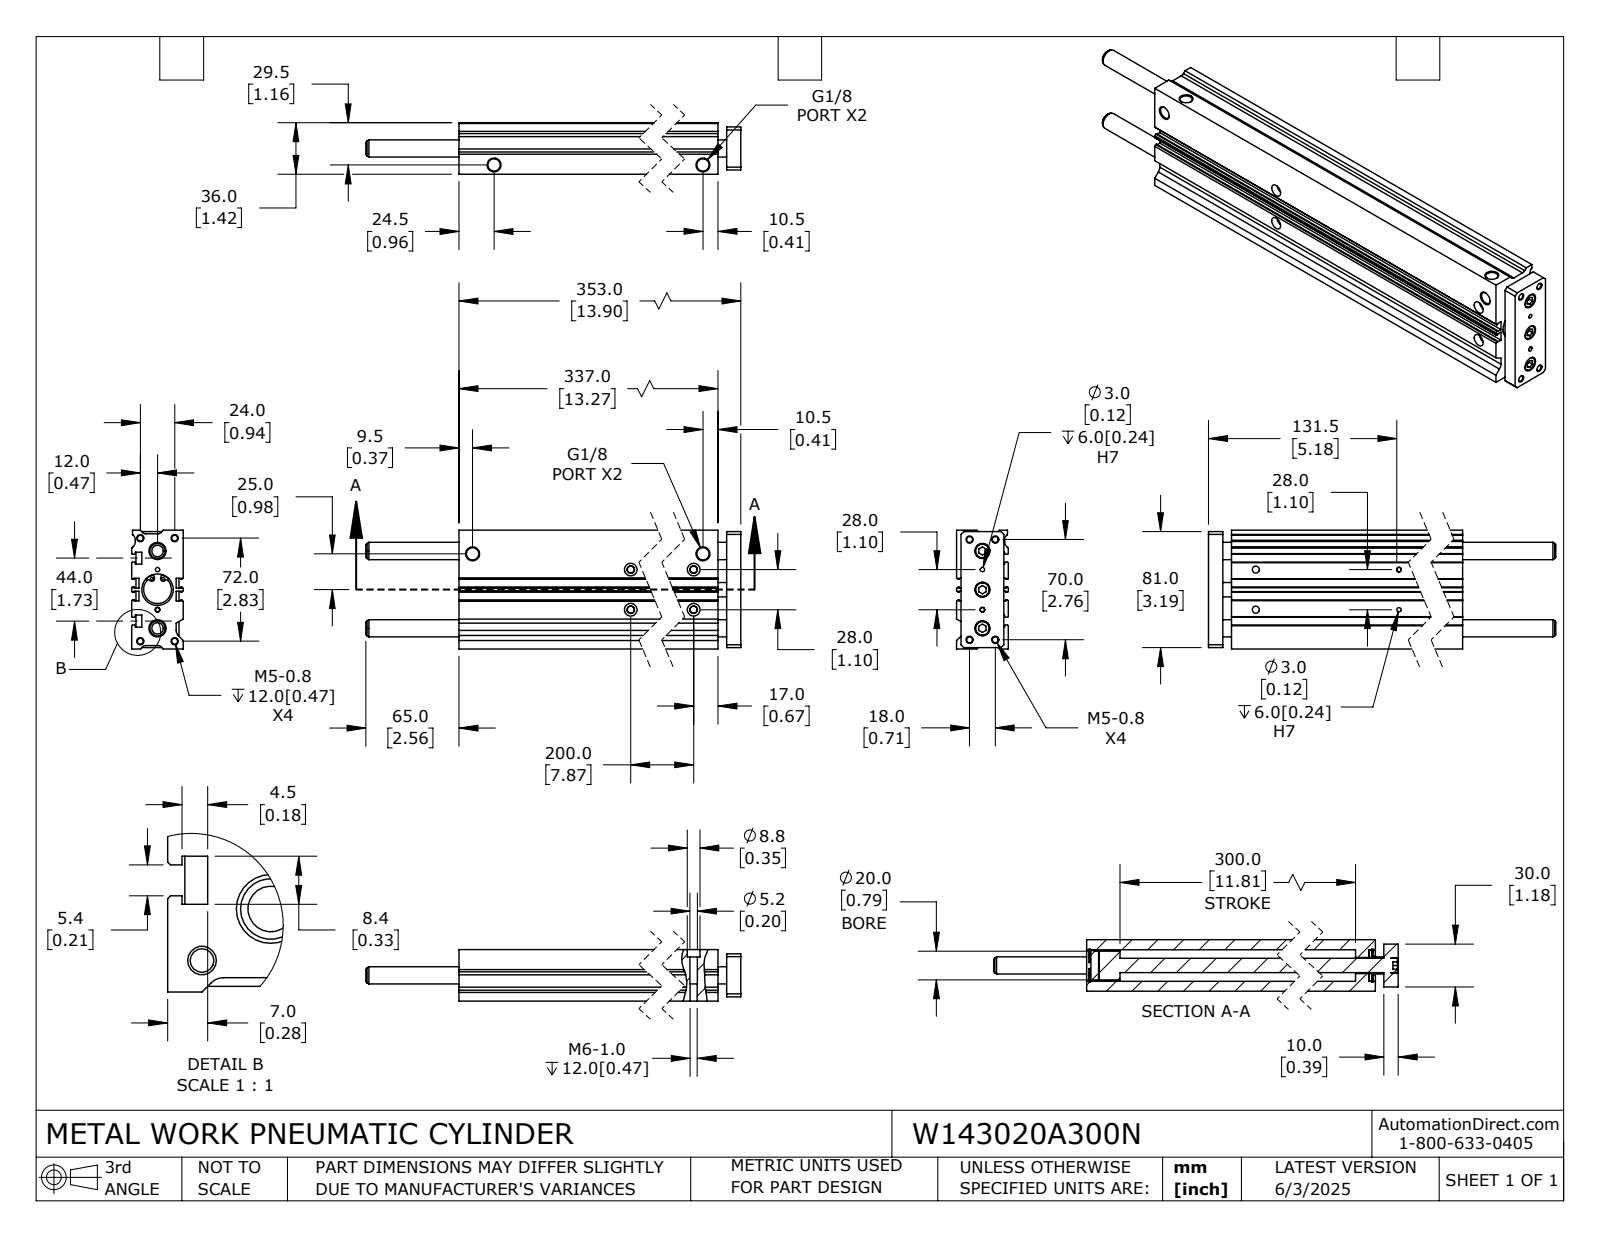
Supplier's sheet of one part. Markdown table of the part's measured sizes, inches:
| quantity | value |
| --- | --- |
| part name | W143020A300N_BODY; W143020A300N; W143020A300N_ROD |
| STEP written by | SolidWorks 2024 (CONFIG_CONTROL_DESIGN) |
| units | inches |
| bodies | 6 solids, 357 faces (174 planar, 145 cylindrical, 38 other) |
| overall size | 16.457 × 3.268 × 1.417 |
| volume | 50.12 in³ |
| surface area | 345.9 in² |
| round holes (diameter × count) | 0.163 × 8, 0.079 × 4, 0.118 × 4, 0.205 × 4, 0.337 × 4, 0.346 × 4, 0.413 × 3, 0.194 × 2, 0.194 × 2, 0.472 × 2, 0.449 × 1, 0.767 × 1 |
| round bosses / shafts (diameter × count) | 0.394 × 3, 0.906 × 2, 0.787 × 1, 0.512 × 1 |
| partial cylindrical surfaces (radius × count) | 0.053 × 4, 0.059 × 4, 0.071 × 4, 0.118 × 4, 0.197 × 3 |
| main face-to-face distances | 1.417, 0.098, 0.197, 1.22, 0.079, 3.268, 3.169, 0.276, 0.945, 1.142 |
| hole center spacings | 0.124, 0.296, 0.336, 0.474, 0.591, 0.78, 0.828, 0.864 |
